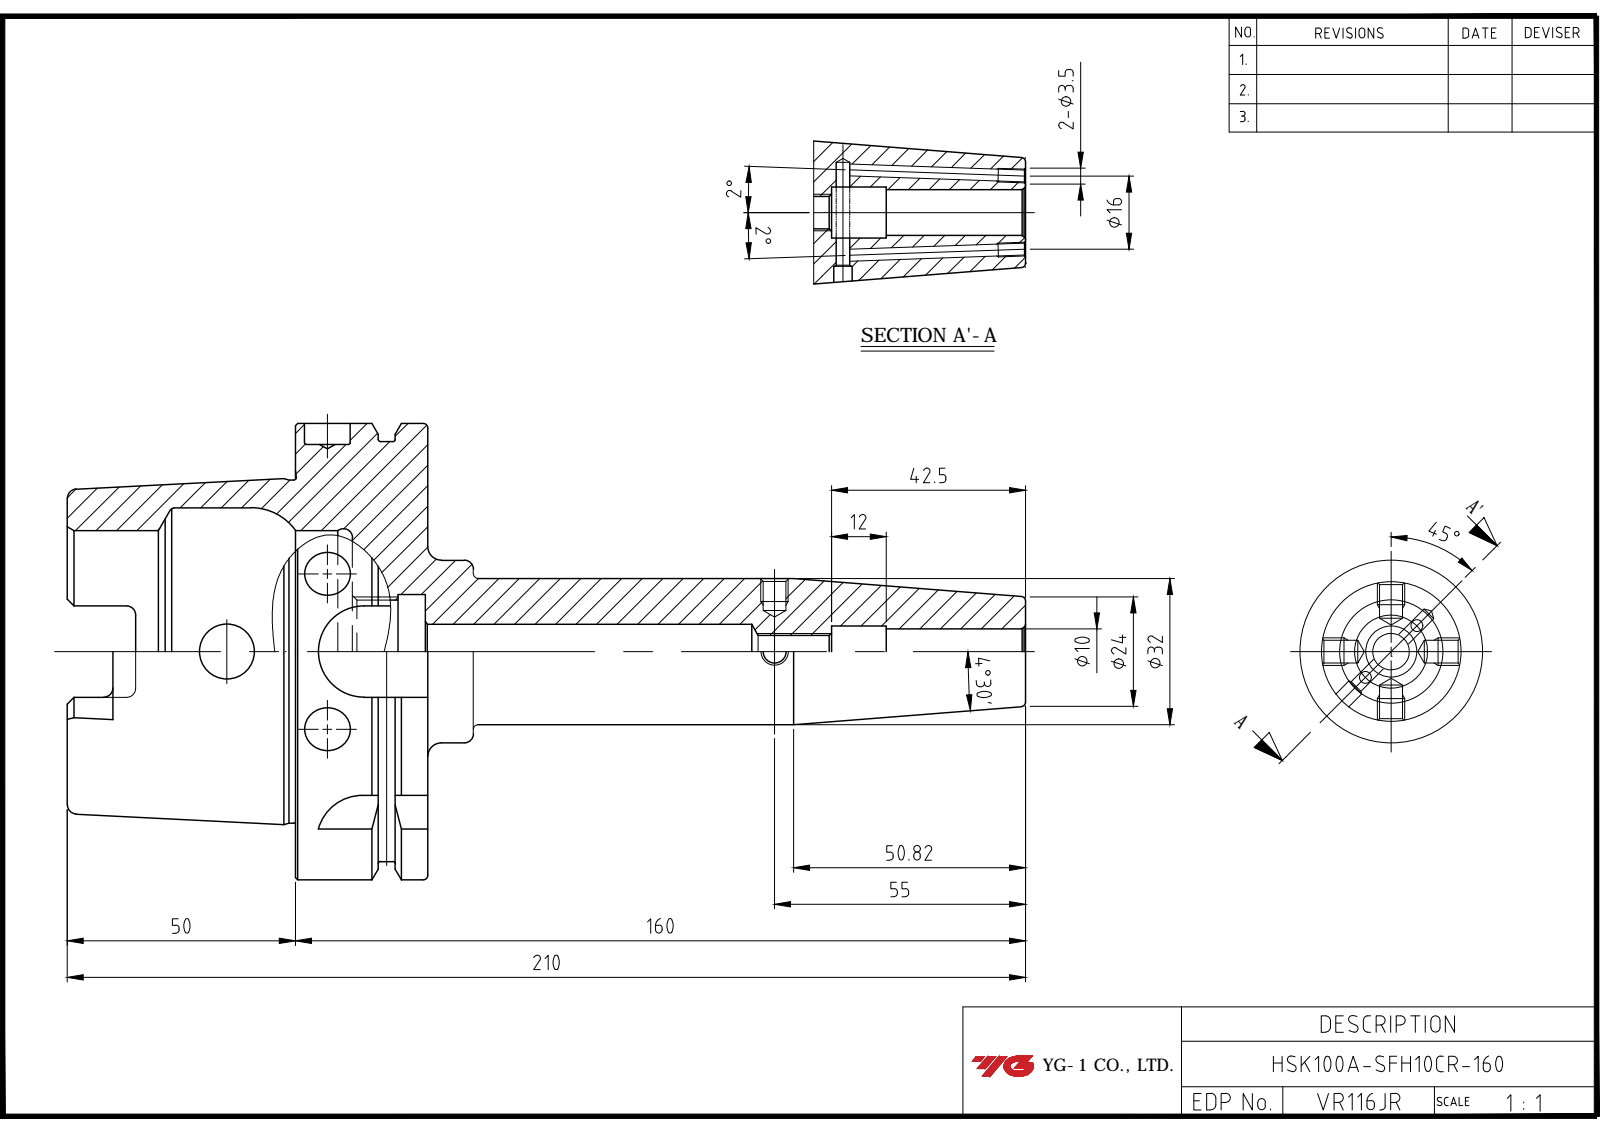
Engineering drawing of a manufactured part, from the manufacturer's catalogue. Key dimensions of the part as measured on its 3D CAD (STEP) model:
Part name (STEP PRODUCT): LO-HSK100A-SFH10CR-160
STEP written by: Autodesk Inventor 2024 (AUTOMOTIVE_DESIGN)
Units: millimetres
Bodies: 1 solid, 123 faces (38 planar, 38 cylindrical, 47 other)
Overall size (bounding box): 210 × 100 × 100
Volume: 342 207 mm³ · Surface area: 66 667 mm²
Round holes (diameter × count): ⌀2.46 ×2, ⌀10 ×2, ⌀12 ×2, ⌀6.92 ×1, ⌀11.2 ×1, ⌀22.38 ×1, ⌀25 ×1, ⌀53 ×1, ⌀63 ×1
Round bosses / shafts (diameter × count): ⌀100 ×1, ⌀92 ×1, ⌀75.41 ×1, ⌀40 ×1, ⌀32 ×1
Partial cylindrical surfaces — rounded edges, fillets, slot ends (radius × count): R2 ×6, R4.88 ×4, R10 ×4
Main face-to-face distances: 29, 12.5, 16.5, 62.5, 50, 79, 88, 78.5, 28.5, 16
